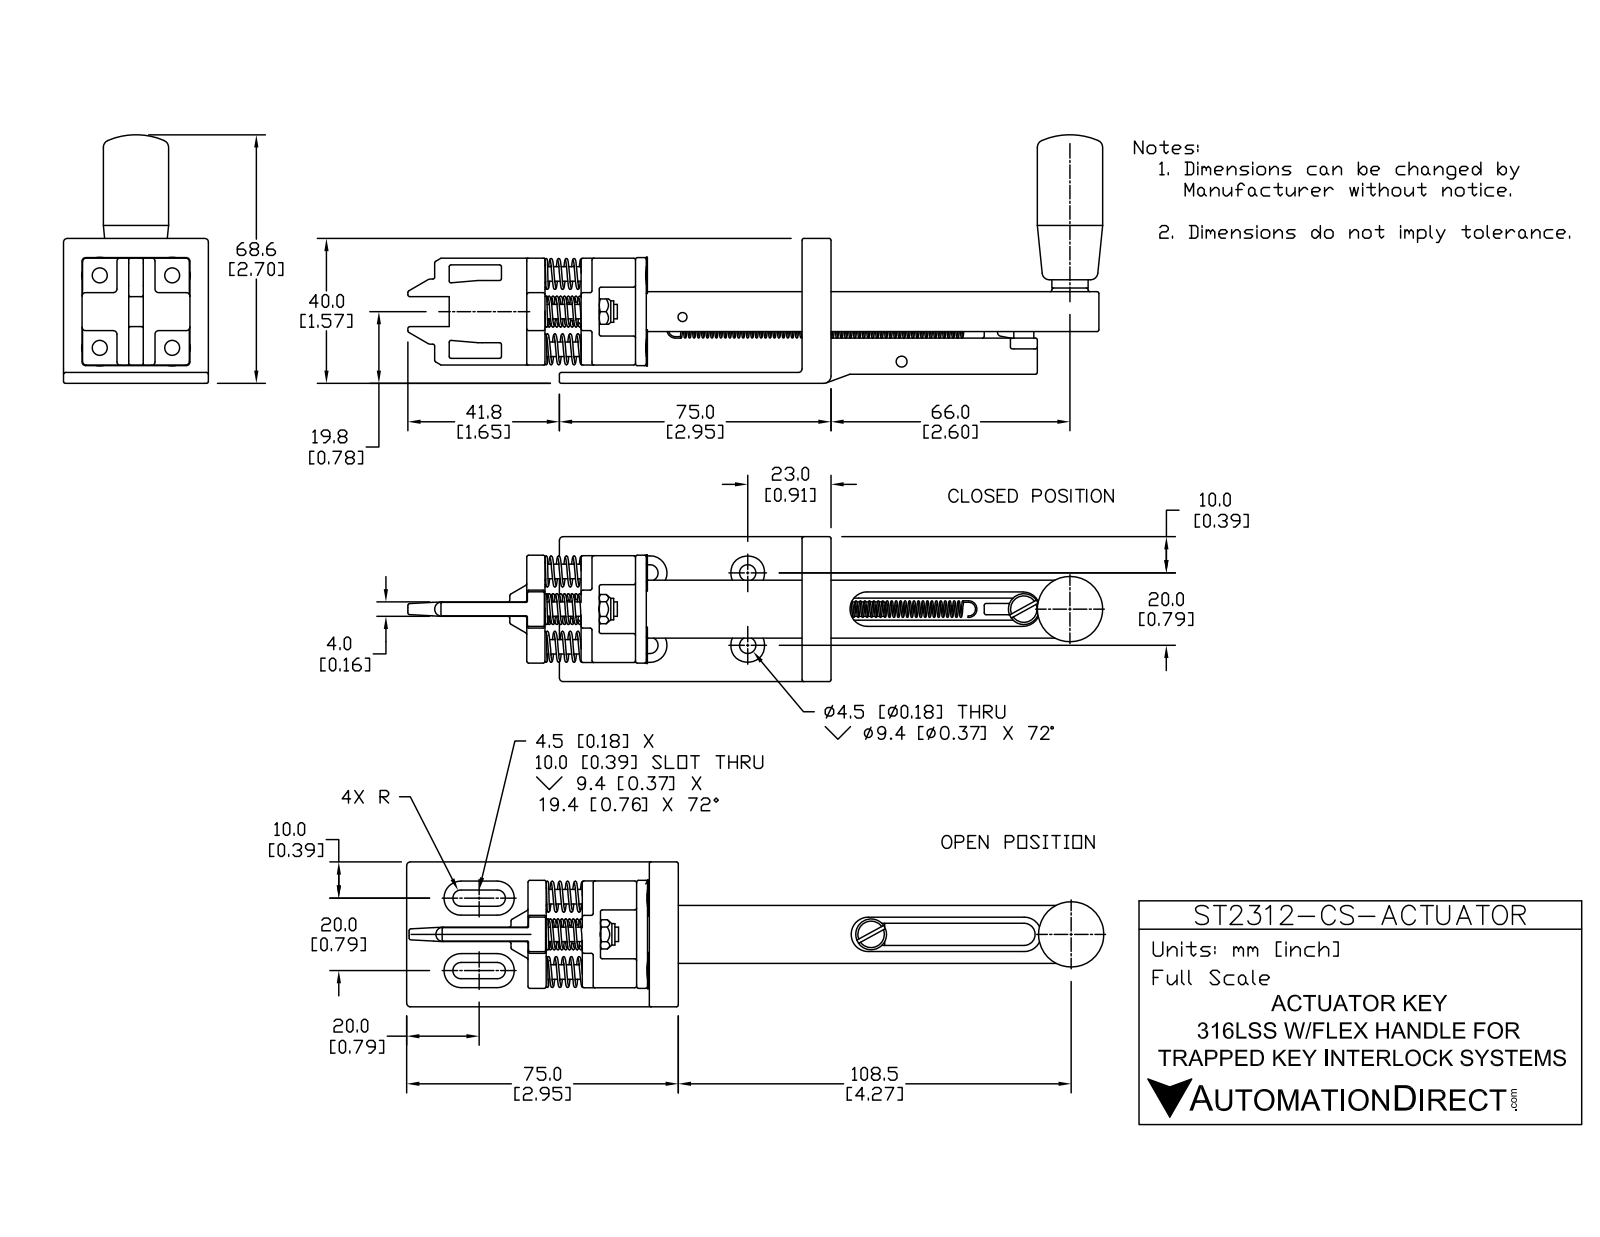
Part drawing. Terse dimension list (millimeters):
name: ST2312-CS-ACTUATOR
written by: SolidWorks 2017 (AUTOMOTIVE_DESIGN)
unit: mm
bodies: 22 solids, 1921 faces (702 planar, 420 cylindrical, 799 other)
size: 191.8 × 67.8 × 40
volume: 45 610 mm³; area: 38 950 mm²
holes: 5× ⌀3.3, 4× ⌀4.1, 4× ⌀5.8, 4× ⌀6, 3× ⌀2, 2× ⌀4.5, 1× ⌀2.5, 1× ⌀3, 1× ⌀4.3, 1× ⌀4.9
bosses: 6× ⌀5, 6× ⌀4, 5× ⌀10, 4× ⌀5.9, 1× ⌀18, 1× ⌀12, 1× ⌀8.5, 1× ⌀6
rounds: 212× R0.5, 55× R1, 12× R0.9, 10× R0.3, 4× R2.3, 4× R6.8, 2× R0.4, 2× R4.7
face distances: 3, 10, 13, 12, 15, 7, 6, 21.5, 8, 25
hole spacings: 10, 22.7, 20, 10.4, 14.1, 14.7, 20.8, 24.2
